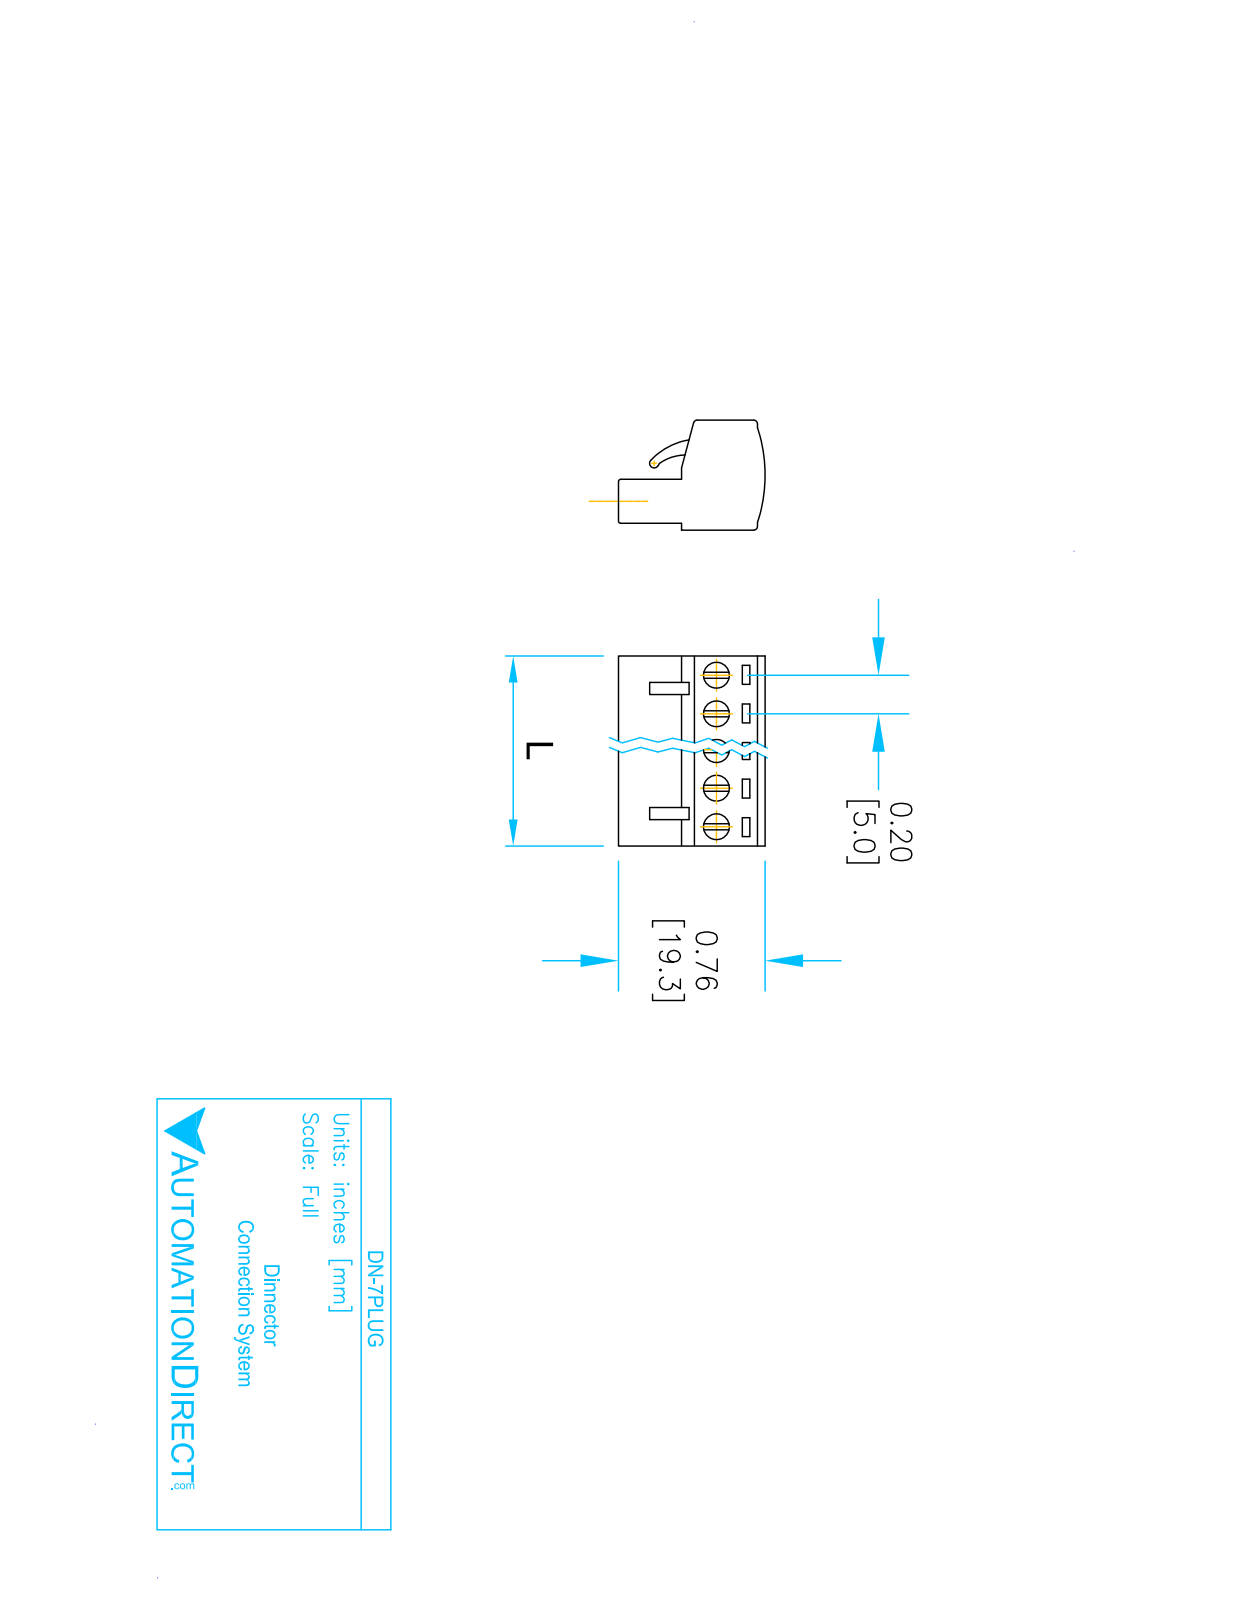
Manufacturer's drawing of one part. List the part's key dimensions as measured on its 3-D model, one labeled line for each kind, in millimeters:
Part name (STEP PRODUCT): 49002_S; 49001_S; 49007_S; 49001_S_49002_SENZA DENTE
STEP written by: SolidWorks 2013 (AUTOMOTIVE_DESIGN)
Units: millimetres
Bodies: 6 solids, 635 faces (445 planar, 155 cylindrical, 35 other)
Overall size (bounding box): 35.56 × 19.3 × 14.5
Volume: 6 083 mm³ · Surface area: 6 207 mm²
Round holes (diameter × count): ⌀1.6 ×7, ⌀2.5 ×7, ⌀3.4 ×7, ⌀3.6 ×7
Round bosses / shafts (diameter × count): ⌀3 ×7
Partial cylindrical surfaces — rounded edges, fillets, slot ends (radius × count): R2.9 ×7, R0.5 ×3, R0.3 ×2, R0.6 ×1, R6 ×1, R9 ×1, R20.03 ×1
Main face-to-face distances: 5.08, 10.16, 15.24, 20.32, 25.4, 6.7, 1, 30.48, 35.56, 14.5
Hole centre spacings: 5.08, 10.16, 15.24, 20.32, 25.4, 30.48
